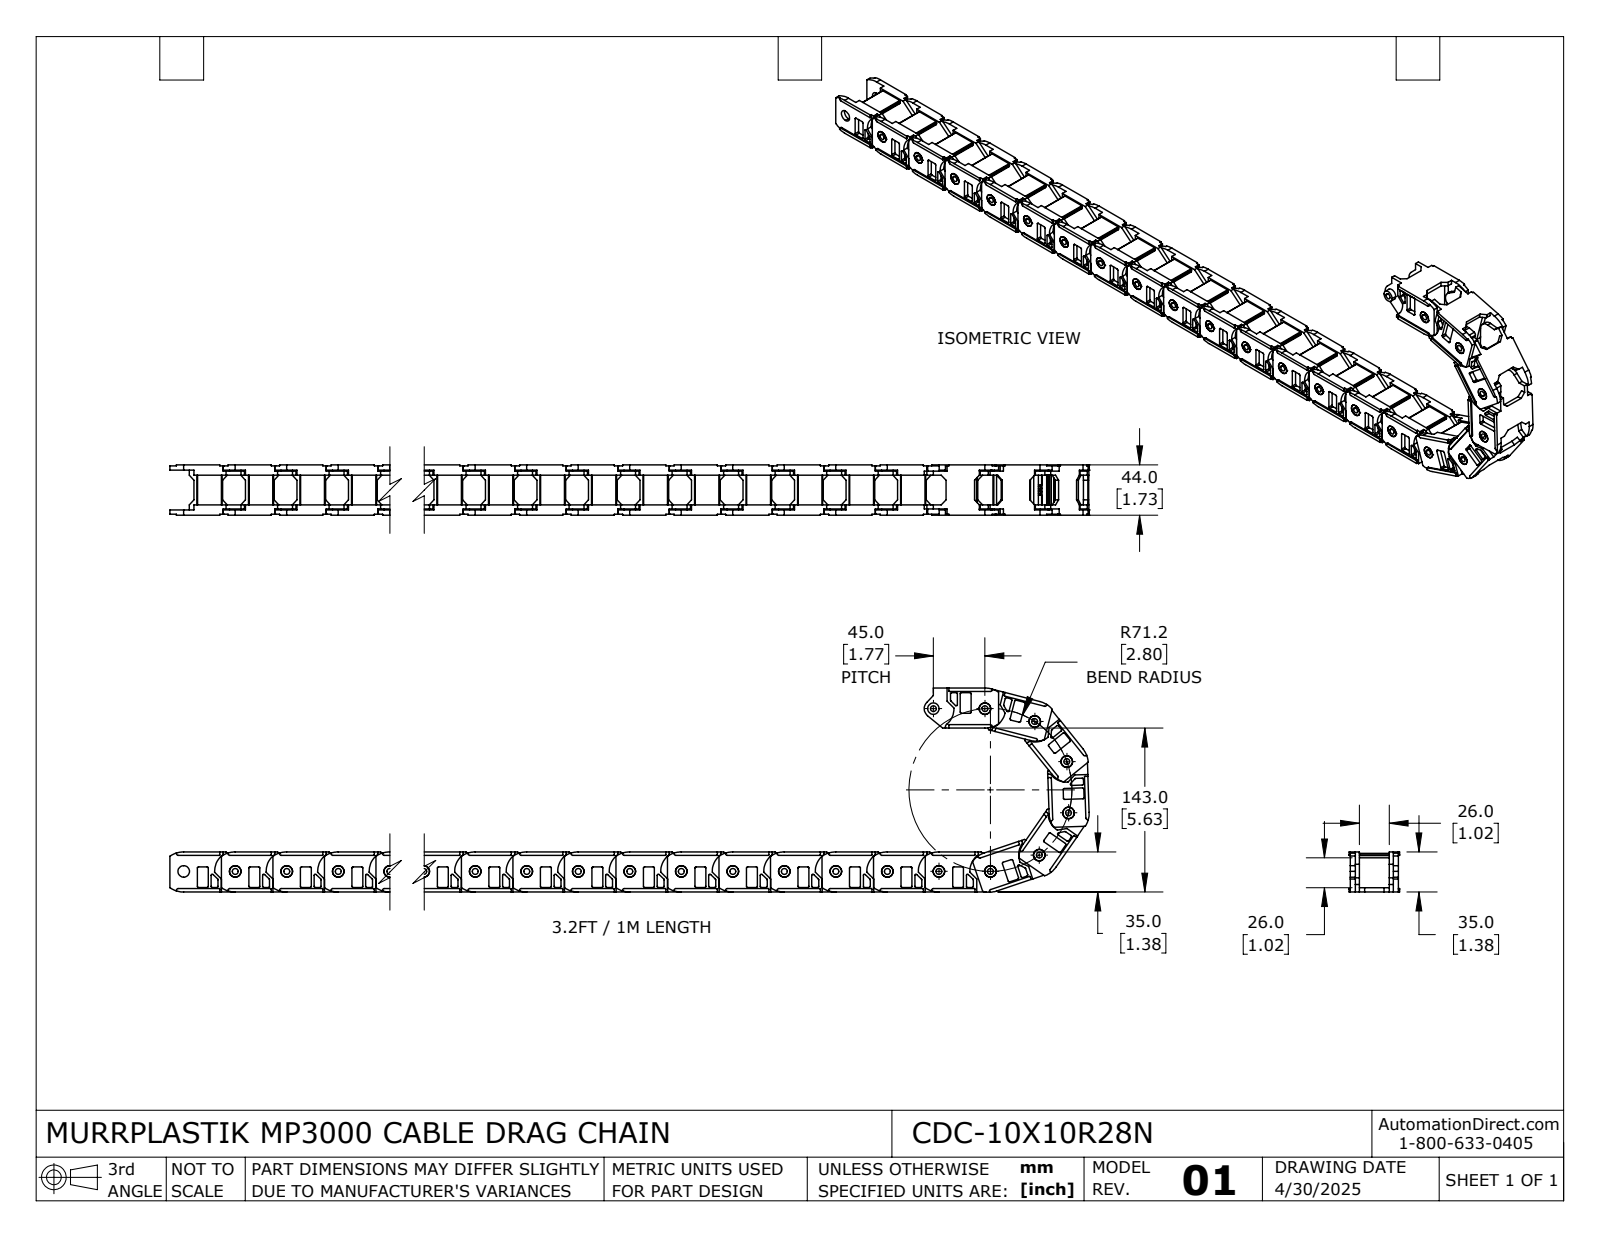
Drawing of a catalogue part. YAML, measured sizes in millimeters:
part_name: "CDC-10X10R28N"
step_written_by: "SolidWorks 2024 (AUTOMOTIVE_DESIGN)"
units: millimeters
bodies: {solids: 22, faces: 3344, planar: 2244, cylindrical: 1100, other: 0}
overall_size: [817.91, 178.19, 44]
volume: 546930
surface_area: 321003
round_holes:
  - {diameter: 5.1, count: 22}
  - {diameter: 10.1, count: 22}
round_bosses_or_shafts:
  - {diameter: 10, count: 22}
partial_cylinders:
  - {radius: 1, count: 176}
  - {radius: 0.5, count: 88}
  - {radius: 1.5, count: 44}
  - {radius: 2, count: 44}
  - {radius: 21, count: 44}
  - {radius: 2.8, count: 22}
  - {radius: 8, count: 22}
  - {radius: 18, count: 22}
face_to_face_distances: [34, 8, 33.8, 26, 4, 30.3, 3.7, 38.3, 4.3, 3.5]
hole_center_spacings: [44.98, 89.96, 45, 134.94, 179.92, 89.98, 224.9, 44.96]
